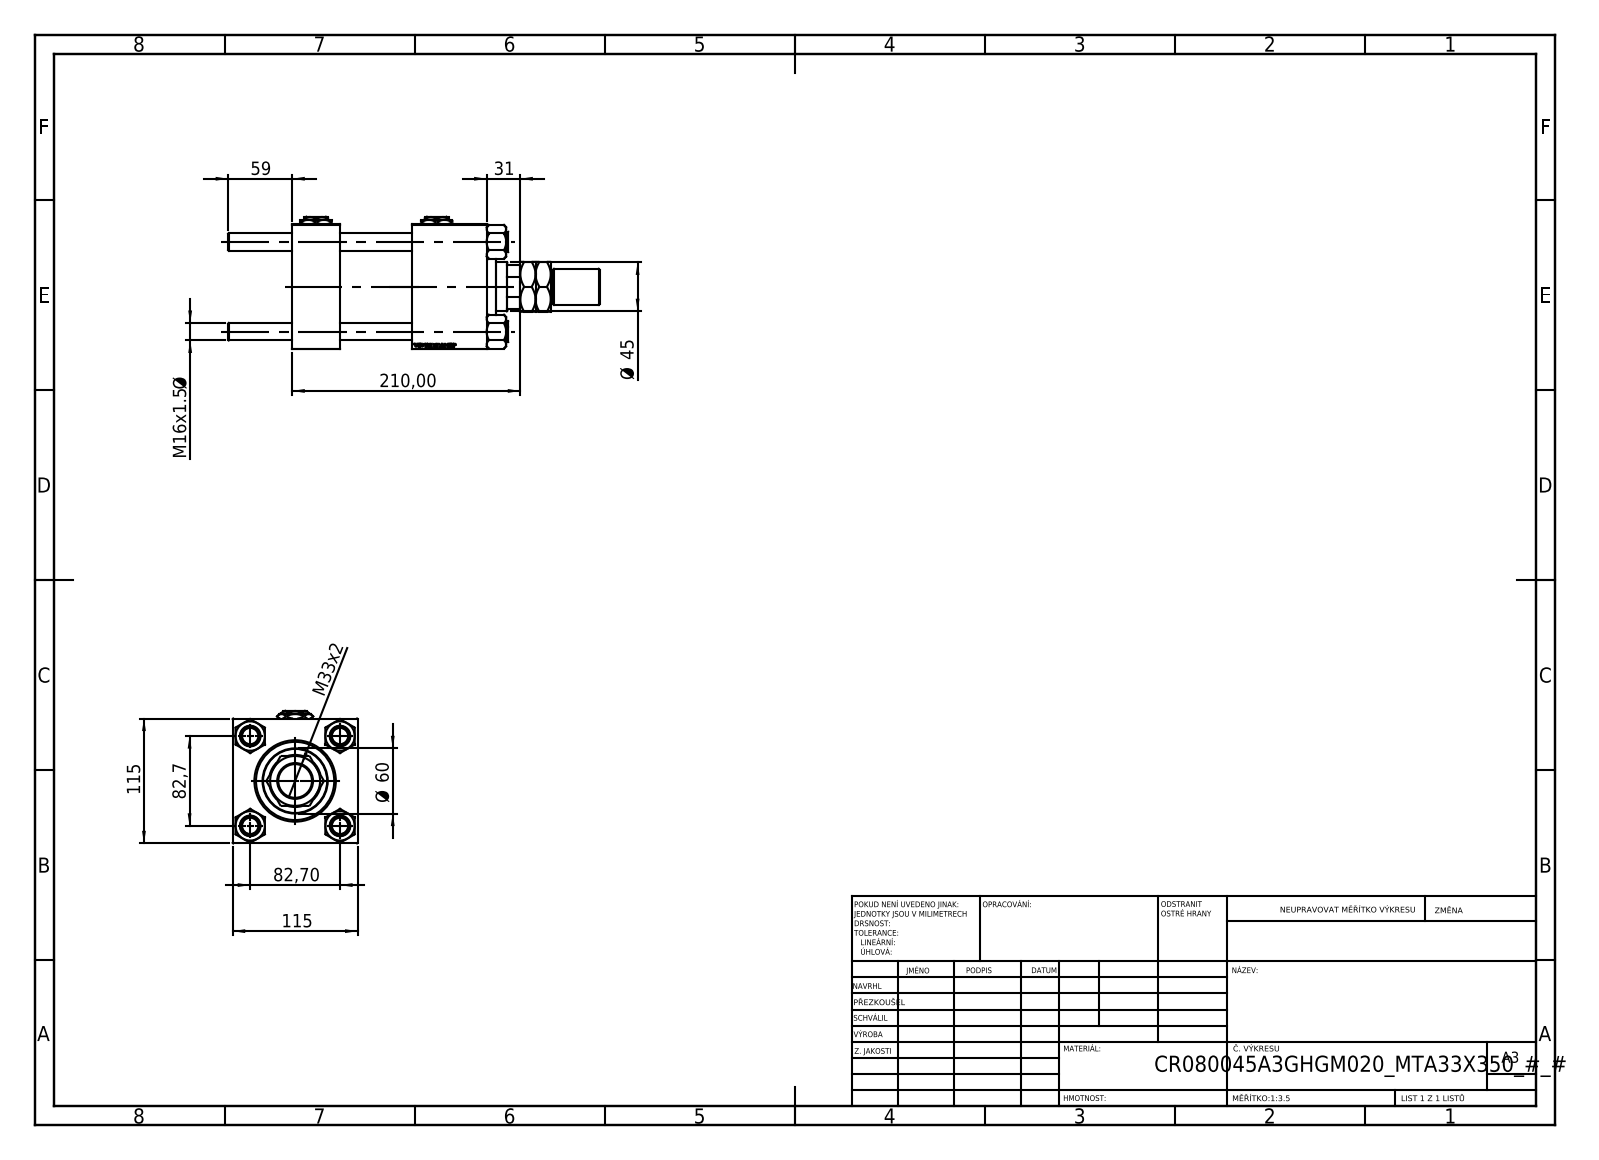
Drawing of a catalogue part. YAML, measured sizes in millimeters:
part_name: "CR025_012_A_0_G_A_G_M_020_+#_##_TYCINKA; V215CR_VCP; MTA; NUT_M5 (+3 more)"
step_written_by: "SolidWorks 2019 (CONFIG_CONTROL_DESIGN)"
units: millimeters
bodies: {solids: 14, faces: 1330, planar: 630, cylindrical: 92, other: 608}
overall_size: [342, 122, 115]
volume: 1973000
surface_area: 319615
round_holes:
  - {diameter: 16, count: 4}
  - {diameter: 7, count: 2}
  - {diameter: 26.44, count: 2}
  - {diameter: 35, count: 2}
  - {diameter: 31.5, count: 1}
  - {diameter: 45, count: 1}
  - {diameter: 48, count: 1}
  - {diameter: 61, count: 1}
  - {diameter: 72, count: 1}
  - {diameter: 80, count: 1}
round_bosses_or_shafts:
  - {diameter: 19, count: 4}
  - {diameter: 86, count: 1}
  - {diameter: 60, count: 1}
  - {diameter: 33, count: 1}
  - {diameter: 31, count: 1}
partial_cylinders:
  - {radius: 22, count: 1}
face_to_face_distances: [115, 44, 179, 135, 110, 69, 66, 46, 20, 89]
hole_center_spacings: [58.48, 82.7, 116.96, 111]
